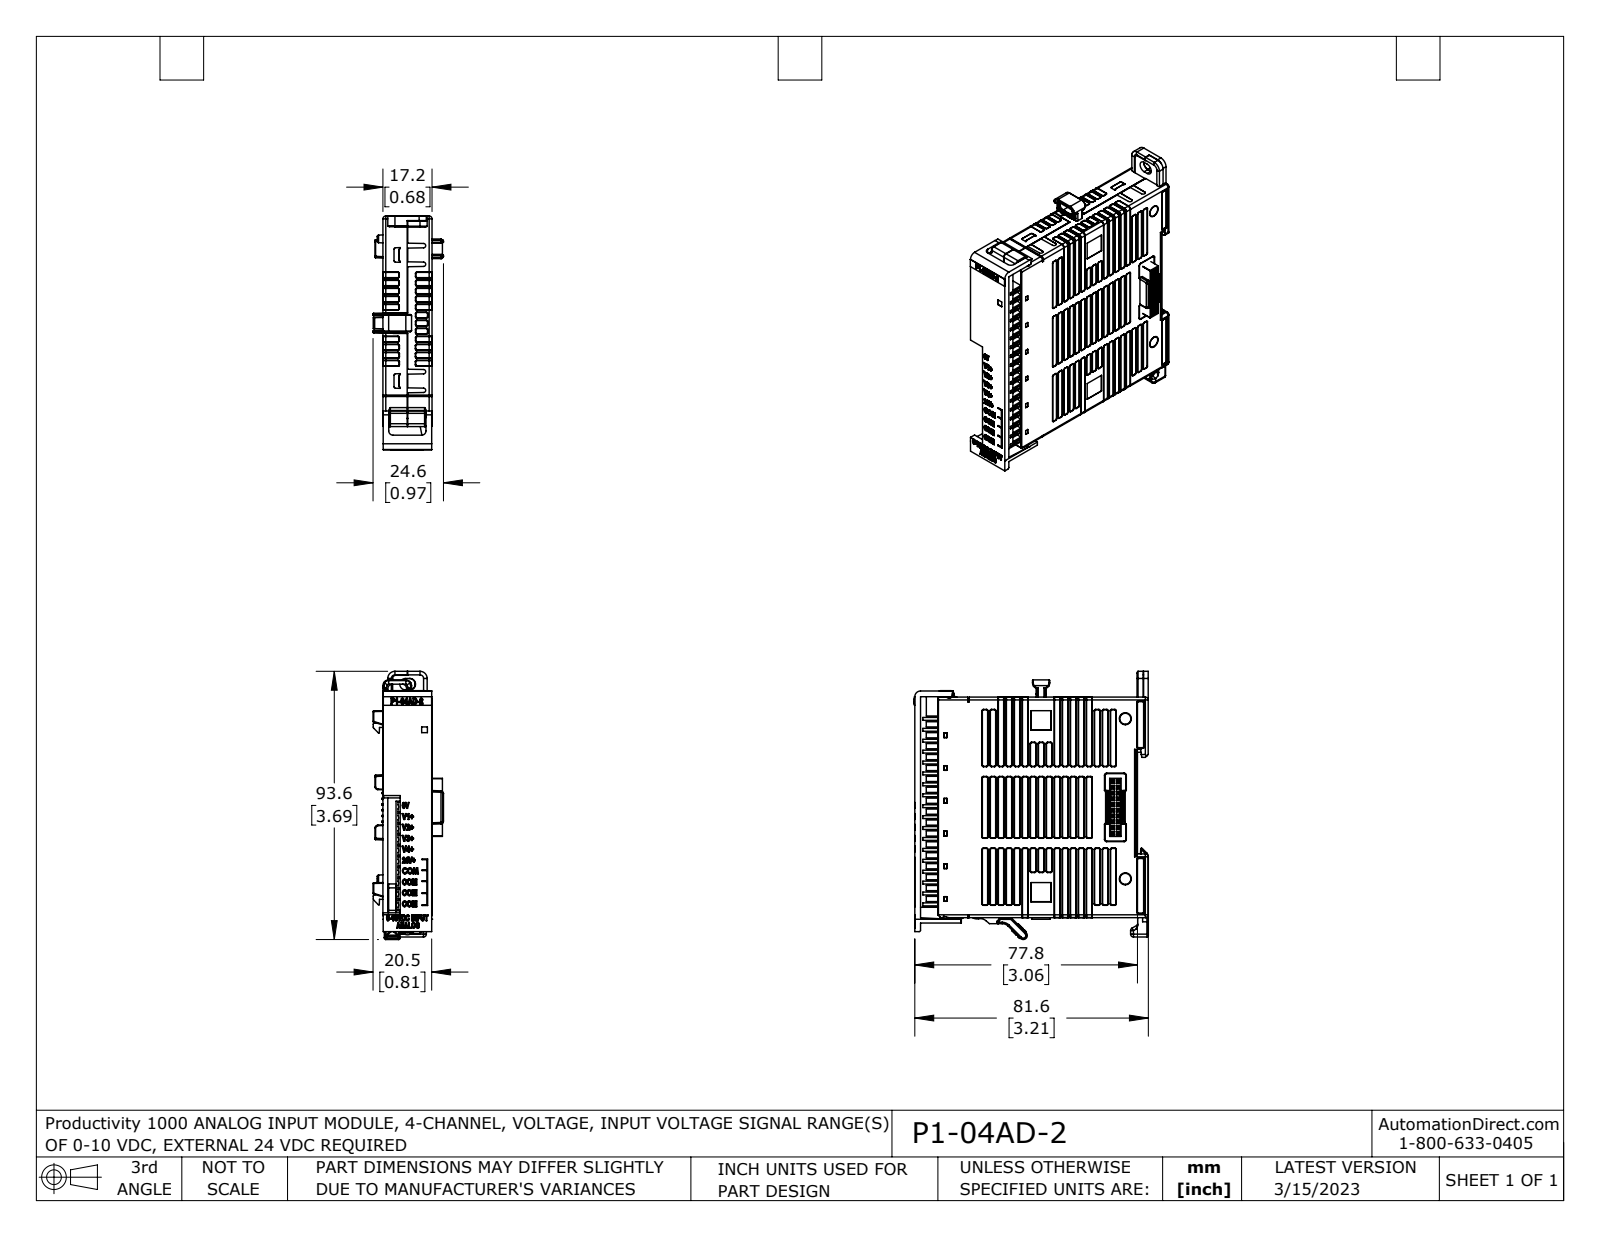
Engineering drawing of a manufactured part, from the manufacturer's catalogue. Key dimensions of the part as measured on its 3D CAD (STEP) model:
Part name (STEP PRODUCT): P1-04AD-2 DIN Coord fxt
STEP written by: SolidWorks 2021 (AUTOMOTIVE_DESIGN)
Units: inches
Bodies: 5 solids, 4777 faces (2609 planar, 1031 cylindrical, 1137 other)
Overall size (bounding box): 3.686 × 3.218 × 1.033
Volume: 5.59 in³ · Surface area: 47.59 in²
Round holes (diameter × count): ⌀0.01 ×20, ⌀0.024 ×8, ⌀0.049 ×1
Round bosses / shafts (diameter × count): ⌀0.043 ×2, ⌀0.064 ×1
Partial cylindrical surfaces — rounded edges, fillets, slot ends (radius × count): R0.01 ×210, R0.02 ×123, R0.039 ×63, R0.079 ×12, R0.059 ×10, R0.008 ×8, R0.03 ×8, R0.03 ×7
Main face-to-face distances: 0.674, 0.675, 0.079, 0.672, 0.315, 2.746, 3.061, 0.236, 0.071, 0.157
Hole centre spacings: 0.079, 0.157, 0.176, 0.236, 0.315, 0.394, 0.402, 0.111
